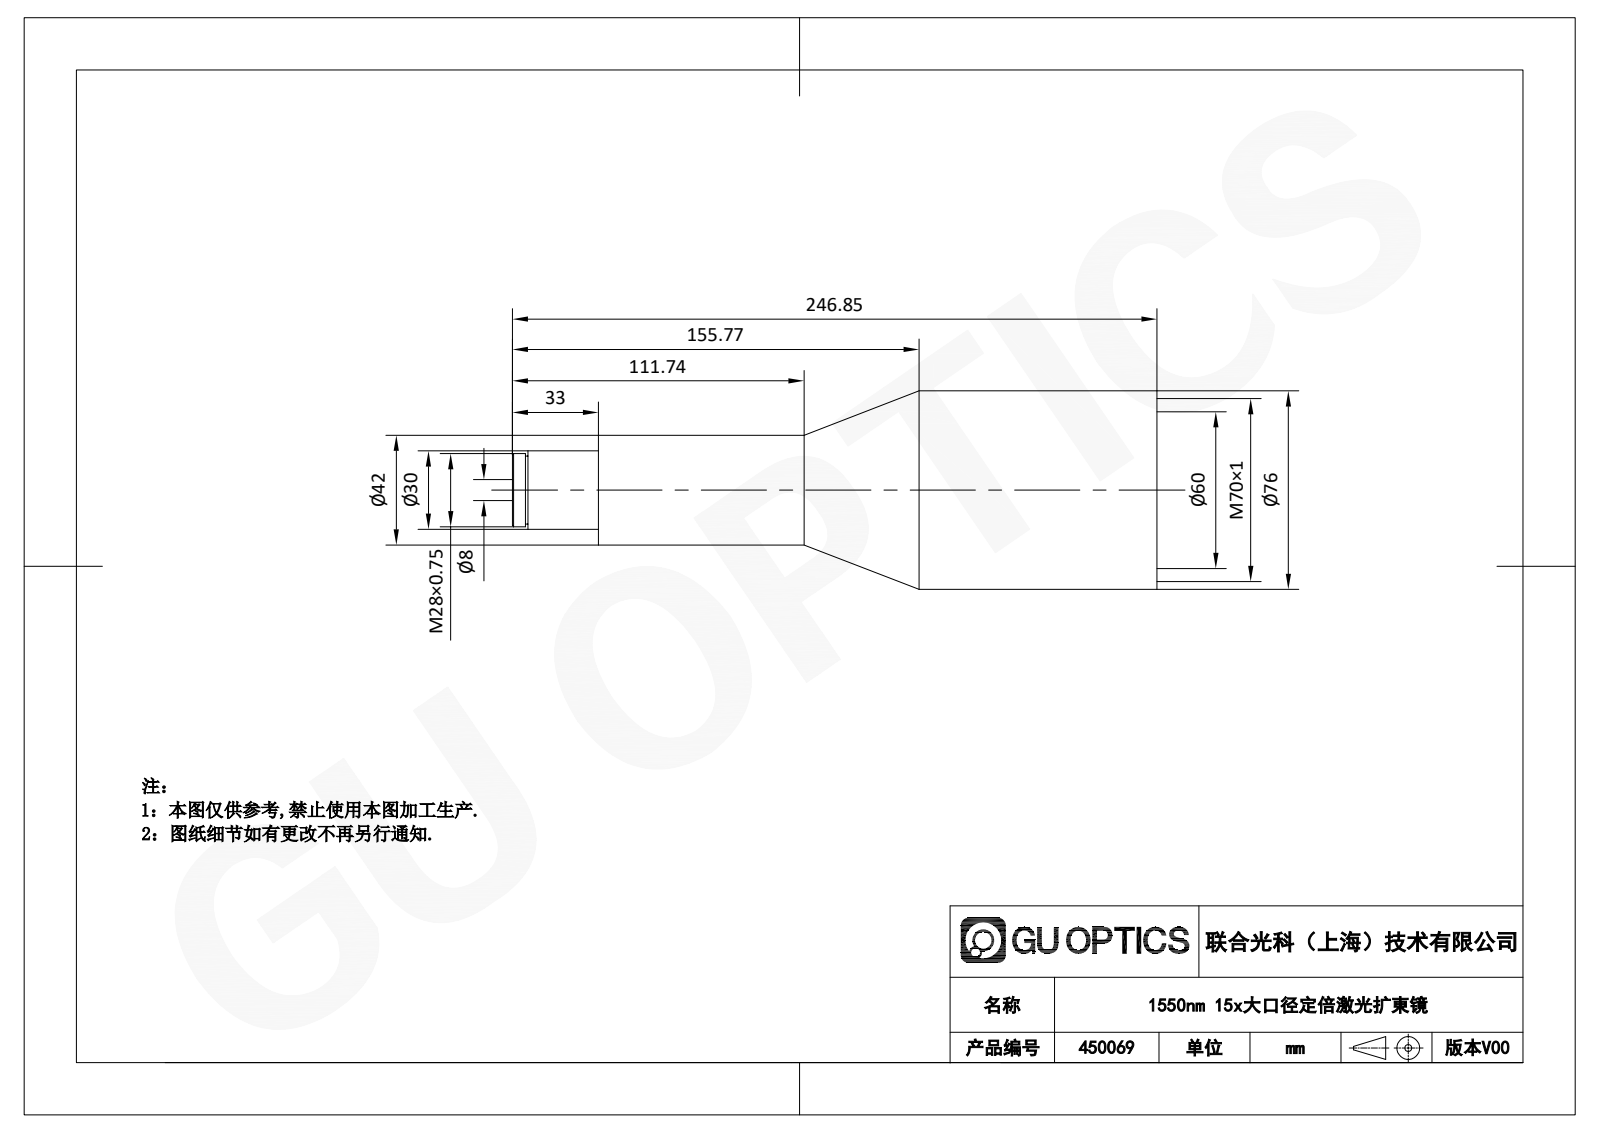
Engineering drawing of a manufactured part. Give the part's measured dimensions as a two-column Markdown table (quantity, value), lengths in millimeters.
| quantity | value |
| --- | --- |
| part name | 450069 |
| STEP written by | SolidWorks 2020 (AUTOMOTIVE_DESIGN) |
| units | millimeters |
| bodies | 1 solid, 28 faces (8 planar, 16 cylindrical, 4 other) |
| overall size | 246.85 × 76 × 76 |
| volume | 667 591 mm³ |
| surface area | 50 449 mm² |
| round holes (diameter × count) | 8 × 1, 70 × 1 |
| round bosses / shafts (diameter × count) | 76 × 1, 60 × 1, 42 × 1, 30 × 1, 28 × 1, 26 × 1 |
| main face-to-face distances | 1, 212.85, 213.85, 245.85, 33, 246.85, 240.85, 6, 27, 239.85 |
